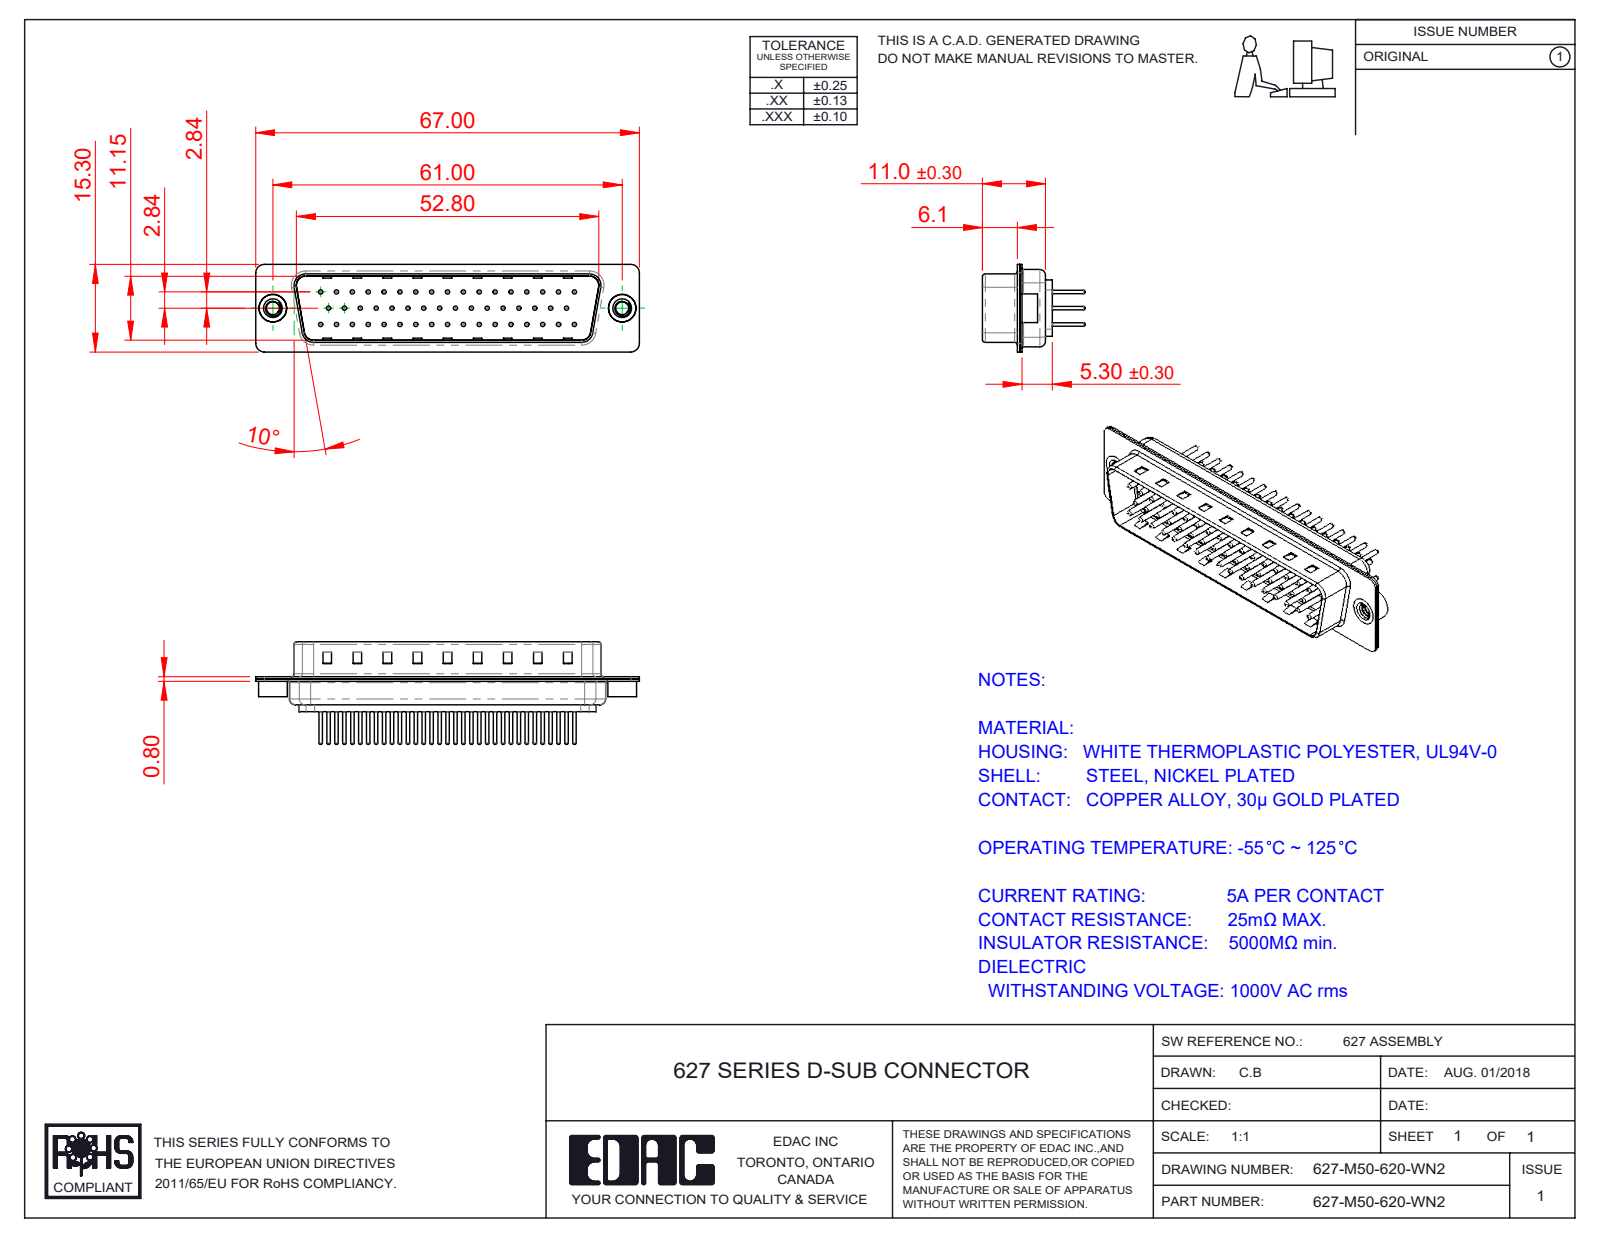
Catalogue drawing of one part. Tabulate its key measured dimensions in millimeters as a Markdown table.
| quantity | value |
| --- | --- |
| part name | 627M Shell Front_50 Contacts; 627M Contact Row 3_20; 627M Contact Row 1_20; 627M 4-40 Threaded Rivet (+4 more) |
| STEP written by | SolidWorks 2020 (CONFIG_CONTROL_DESIGN) |
| units | millimeters |
| bodies | 55 solids, 2262 faces (553 planar, 841 cylindrical, 868 other) |
| overall size | 67 × 17.9 × 15.3 |
| volume | 4 525 mm³ |
| surface area | 10 699 mm² |
| round holes (diameter × count) | 0.75 × 50, 1.6 × 50, 2 × 50, 2.26 × 2, 4 × 2, 4.8 × 2 |
| round bosses / shafts (diameter × count) | 1.5 × 50, 0.6 × 50, 5 × 2, 4.9 × 2 |
| partial cylindrical surfaces (radius × count) | 1.5 × 16, 2 × 12, 0.5 × 8, 1.6 × 8, 0.25 × 4, 0.6 × 4, 0.65 × 4, 0.9 × 4 |
| main face-to-face distances | 0.4, 11.55, 5.7, 6.1, 0.78, 0.77, 12.33, 12.32, 13.1, 5.3 |
| hole center spacings | 3.16, 2.77, 5.54, 8.31, 11.08, 13.85, 16.62, 5.03 |
